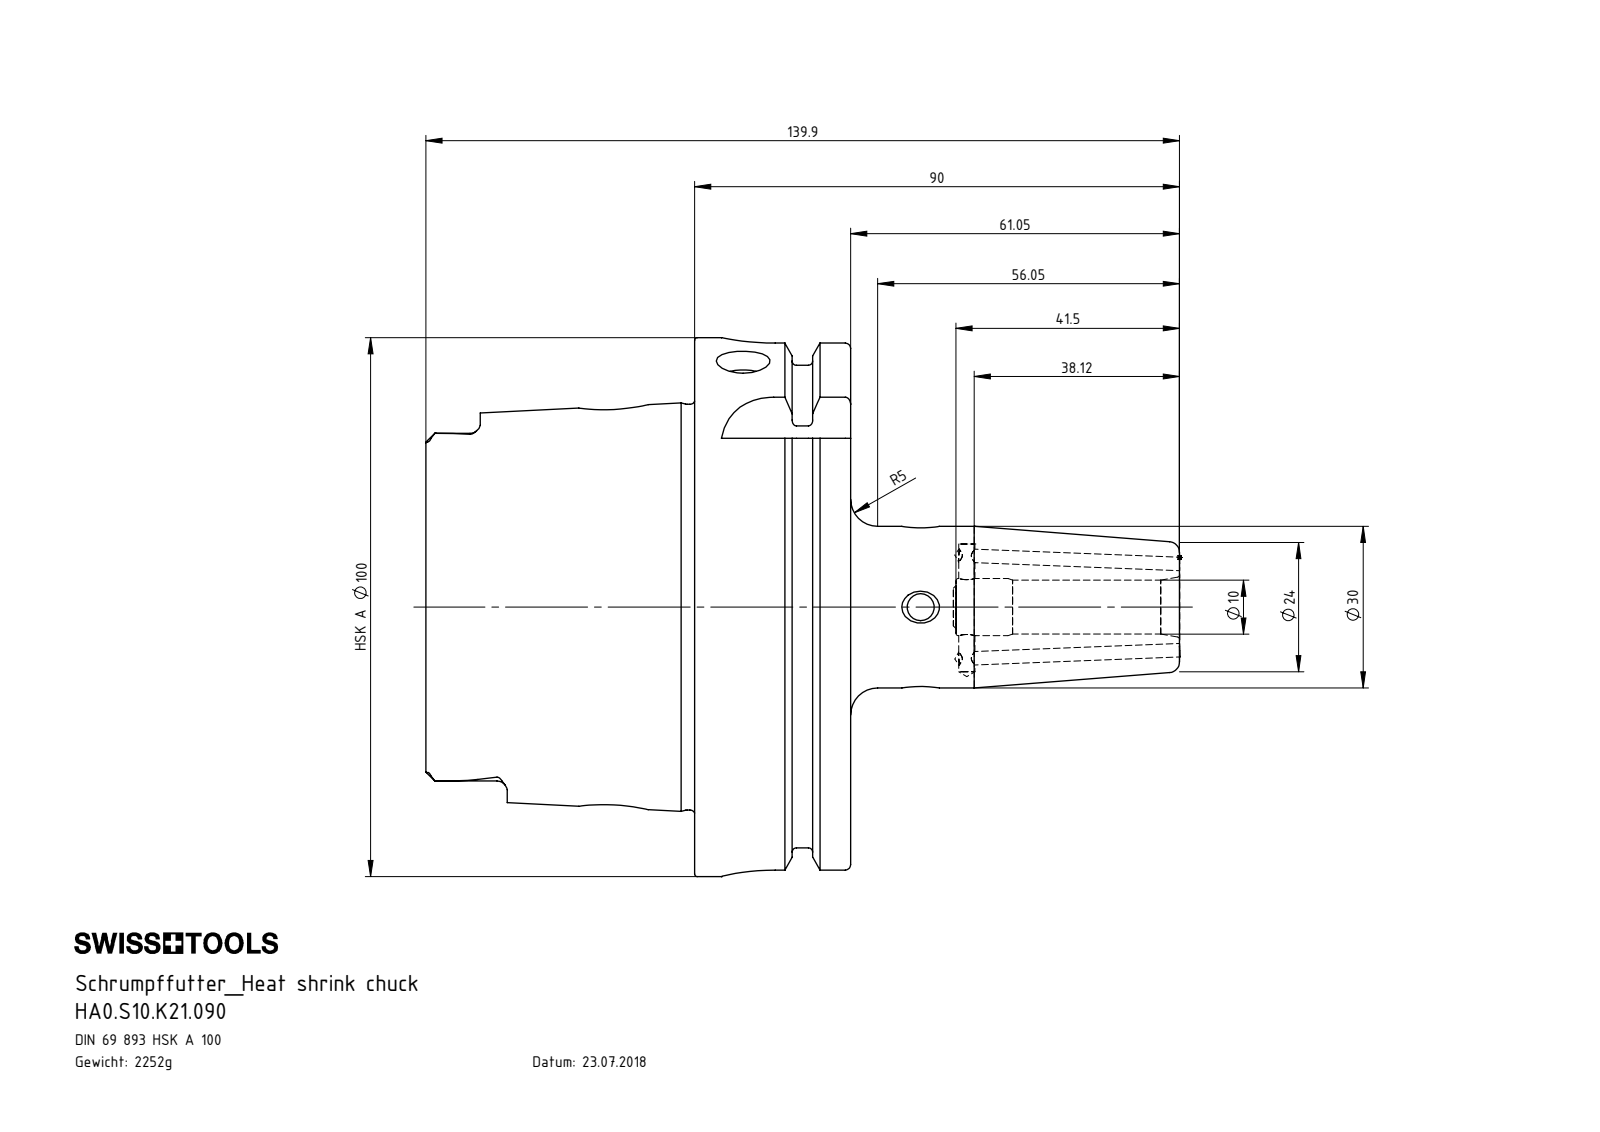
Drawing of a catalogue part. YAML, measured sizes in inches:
part_name: "ERU-CJ2.001.006; ERU-AN3.K01.020_A; HA0-S10.K21.090_C_Fertigbearbeitung; HA0.S10.K21.090"
step_written_by: "SolidWorks 2017 (AUTOMOTIVE_DESIGN)"
units: inches
bodies: {solids: 4, faces: 292, planar: 95, cylindrical: 86, other: 111}
overall_size: [5.511, 3.937, 3.937]
volume: 17.51
surface_area: 90.85
round_holes:
  - {diameter: 0.394, count: 4}
  - {diameter: 0.098, count: 2}
  - {diameter: 0.197, count: 2}
  - {diameter: 0.118, count: 1}
  - {diameter: 0.157, count: 1}
  - {diameter: 0.276, count: 1}
  - {diameter: 0.417, count: 1}
  - {diameter: 0.472, count: 1}
  - {diameter: 0.886, count: 1}
  - {diameter: 1.024, count: 1}
  - {diameter: 2.087, count: 1}
  - {diameter: 2.48, count: 1}
round_bosses_or_shafts:
  - {diameter: 0.118, count: 2}
  - {diameter: 3.937, count: 1}
  - {diameter: 3.62, count: 1}
  - {diameter: 2.963, count: 1}
  - {diameter: 1.181, count: 1}
  - {diameter: 0.315, count: 1}
partial_cylinders:
  - {radius: 0.075, count: 6}
  - {radius: 0.192, count: 4}
  - {radius: 0.394, count: 4}
face_to_face_distances: [1.14, 0.65, 0.49, 1.965, 2.455, 3.104, 3.079, 1.114, 0.624, 0.026]
hole_center_spacings: [0.337, 1.376, 2.242, 2.579]
